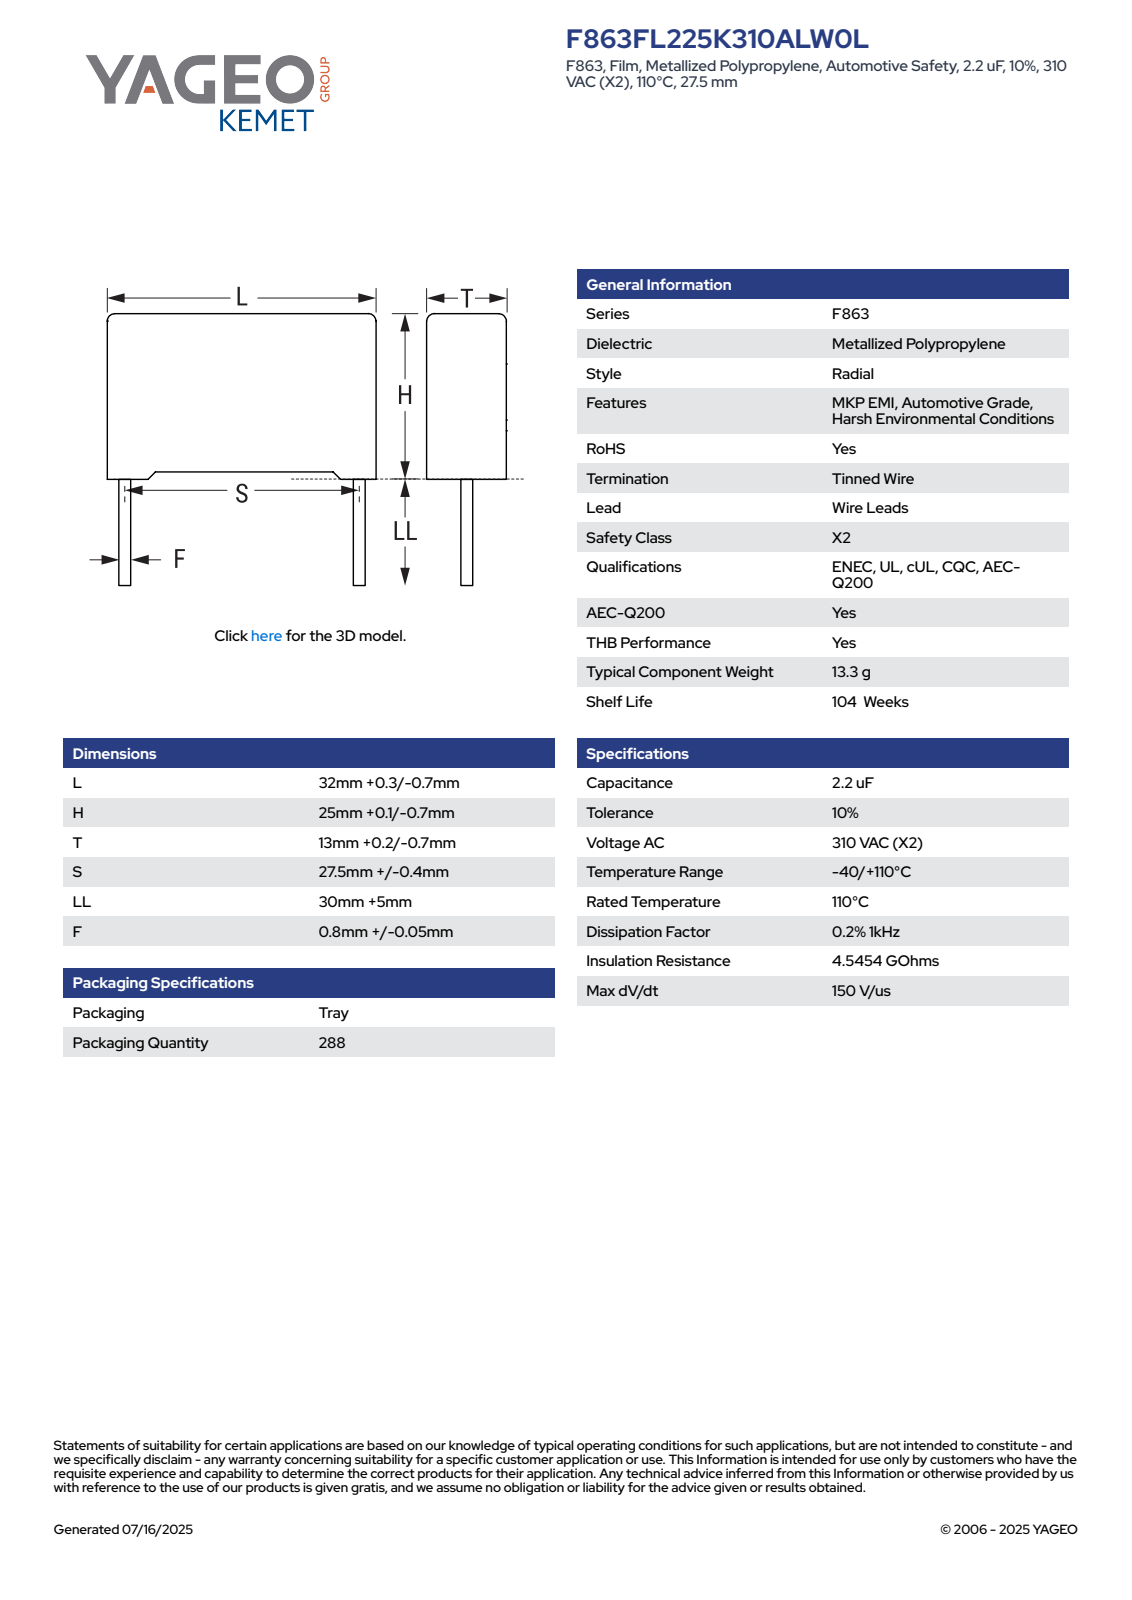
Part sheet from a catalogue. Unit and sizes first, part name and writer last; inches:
Units: inches
Overall size (bounding box): 2.366 × 1.272 × 0.52
Round bosses / shafts (diameter × count): ⌀0.033 ×2
Partial cylindrical surfaces — rounded edges, fillets, slot ends (radius × count): R0.035 ×4
Main face-to-face distances: 0.52, 0.944, 1.272, 0.52, 0.024, 0.496, 0.024, 0.472, 0.496, 0.044
Volume: 0.626 in³ · Surface area: 5.129 in²
Bodies: 4 solids, 89 faces (81 planar, 8 cylindrical, 0 other)
Part name (STEP PRODUCT): CFR_RB_32X25X13_L32.3H25.1T13.2S27.5LL35F0.85
STEP written by: SolidWorks 2014 (AUTOMOTIVE_DESIGN)
